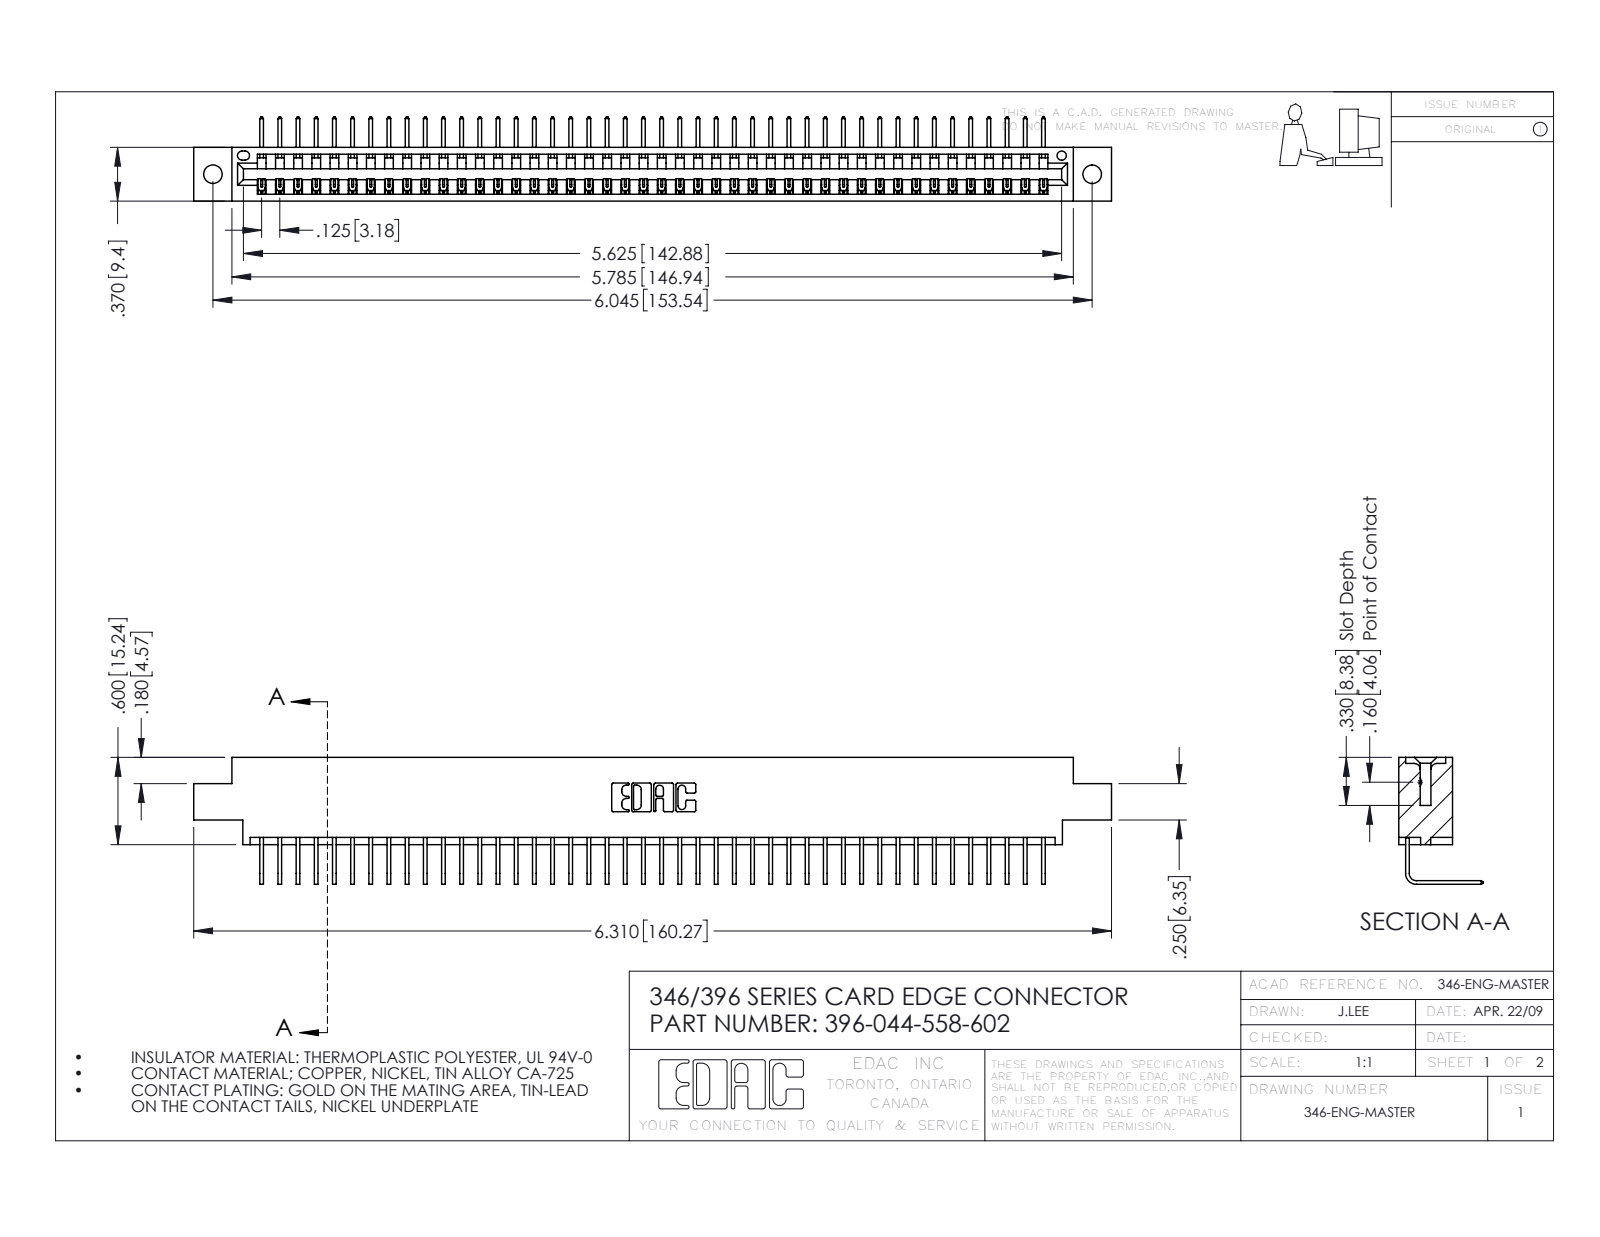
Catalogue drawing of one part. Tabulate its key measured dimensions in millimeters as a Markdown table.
| quantity | value |
| --- | --- |
| part name | 345-292-001_558 Tail - 2; 346 Part_0.170 Offset - 0.128 Dia; 396-044-558-602 |
| STEP written by | SolidWorks 2016 (CONFIG_CONTROL_DESIGN) |
| units | millimeters |
| bodies | 45 solids, 2766 faces (1928 planar, 838 cylindrical, 0 other) |
| overall size | 160.3 × 22.2 × 14.7 |
| volume | 15 300 mm³ |
| surface area | 19 920 mm² |
| round holes (diameter × count) | 3.3 × 2, 1.6 × 1 |
| partial cylindrical surfaces (radius × count) | 0.2 × 88, 0.3 × 22, 0.2 × 6, 0.8 × 6, 0.7 × 3, 0.8 × 2, 1 × 2, 0.4 × 1 |
| main face-to-face distances | 8.2, 1.2, 9.4, 6.4, 7.6, 0.6, 1.8, 3.8, 5.6, 2.5 |
| hole center spacings | 6.2, 148.2, 153.5 |
